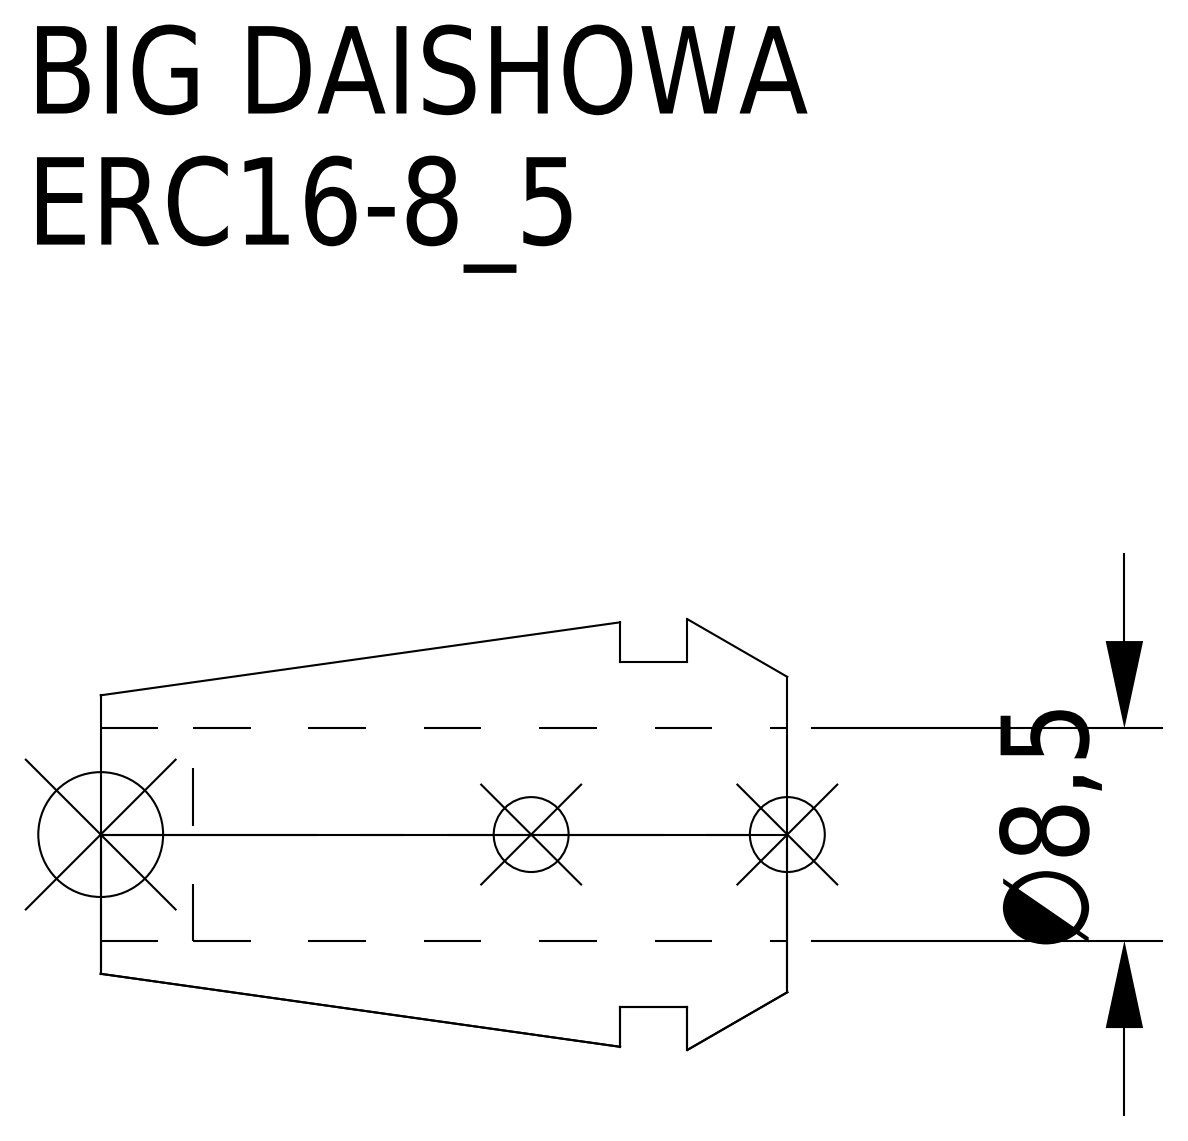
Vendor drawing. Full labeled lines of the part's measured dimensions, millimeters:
Part name (STEP PRODUCT): ERC16-8_5
STEP written by: CREO PARAMETRIC BY PTC INC, 2016380 (AUTOMOTIVE_DESIGN)
Units: millimetres
Bodies: 1 solid, 15 faces (5 planar, 6 cylindrical, 4 other)
Overall size (bounding box): 27.5 × 17.25 × 17.25
Volume: 2 832 mm³ · Surface area: 2 269 mm²
Round holes (diameter × count): ⌀8.5 ×1, ⌀8.55 ×1
Round bosses / shafts (diameter × count): ⌀13.8 ×1
Main face-to-face distances: 2.7, 4, 6.7, 27.5, 23.5, 20.8, 23.8, 19.8, 17.1, 3.7
